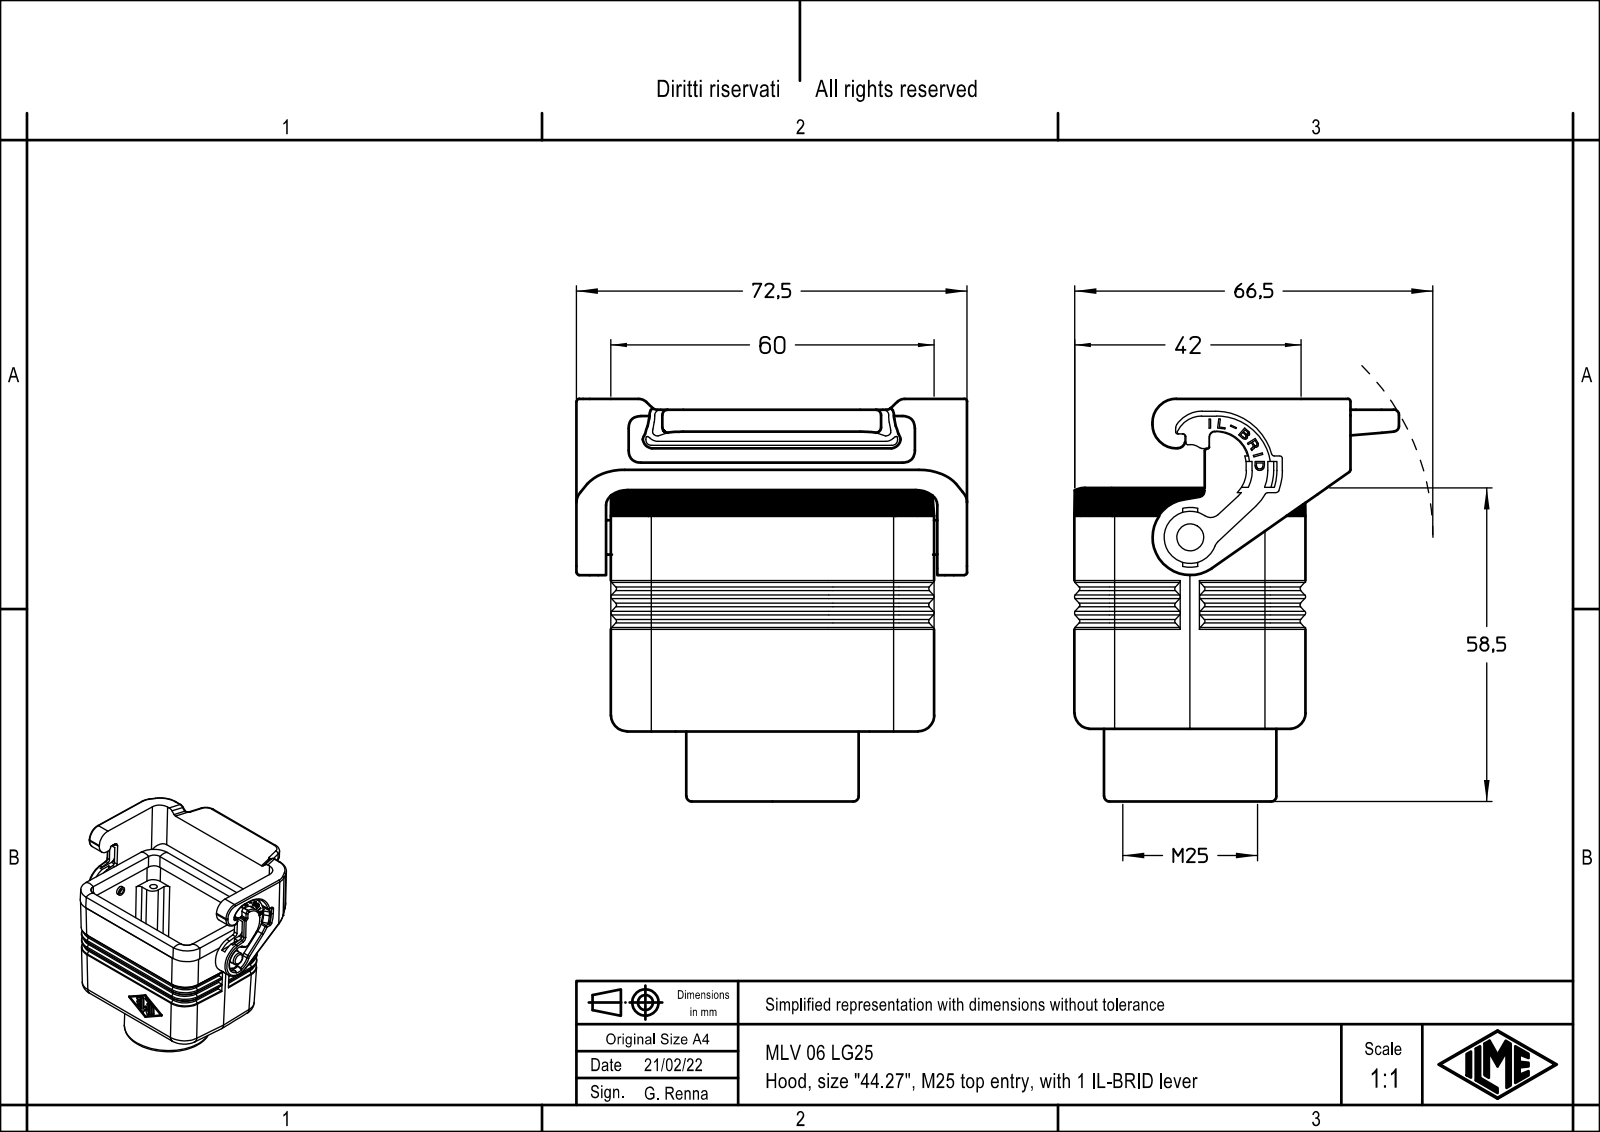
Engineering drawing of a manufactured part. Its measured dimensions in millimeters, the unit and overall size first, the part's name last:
Units: millimetres
Overall size (bounding box): 74.7 × 72.5 × 60.25
Round holes (diameter × count): ⌀2.75 ×4, ⌀21 ×1, ⌀23.6 ×1
Round bosses / shafts (diameter × count): ⌀32 ×1, ⌀6.4 ×1, ⌀4.8 ×1
Partial cylindrical surfaces — rounded edges, fillets, slot ends (radius × count): R0.5 ×31, R1.5 ×18, R0.33 ×15, R1 ×15, R3 ×12, R7 ×6, R0.3 ×4, R2 ×4
Main face-to-face distances: 3.5, 39.5, 56.5, 3.4, 36, 0.75, 4.25, 57.25, 60.75, 43
Hole centre spacings: 25.81, 27, 44, 51.62
Volume: 55 879 mm³ · Surface area: 31 219 mm²
Bodies: 1 solid, 830 faces (518 planar, 220 cylindrical, 92 other)
Part name (STEP PRODUCT): MLV_06_LG25
STEP written by: Creo Elements/Direct Modeling 20.1B 02-Apr-2019 (C) Parametric Technology GmbH (AUTOMOTIVE_DESIGN)
